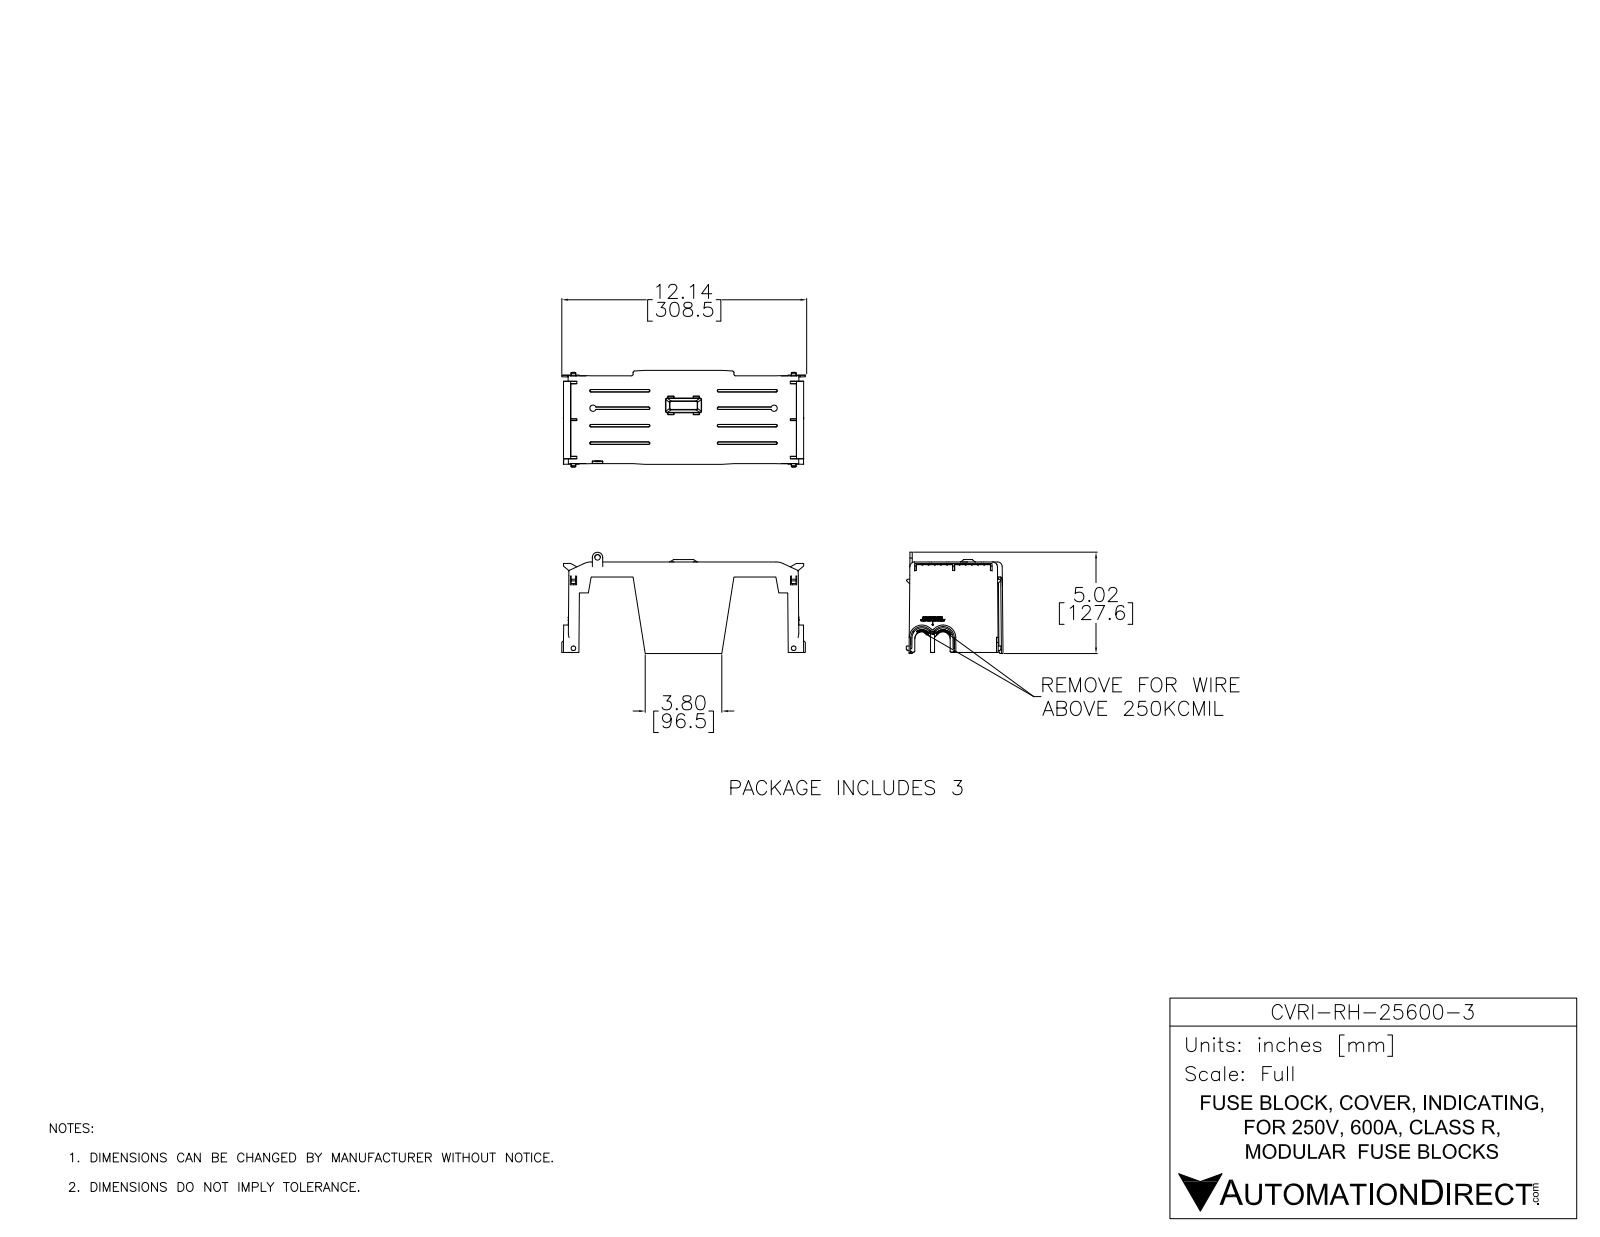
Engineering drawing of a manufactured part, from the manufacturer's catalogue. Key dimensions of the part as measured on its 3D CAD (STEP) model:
Part name (STEP PRODUCT): CVRI-RH-25600-3
STEP written by: SolidWorks 2017 (AUTOMOTIVE_DESIGN)
Units: inches
Bodies: 1 solid, 2344 faces (1576 planar, 119 cylindrical, 649 other)
Overall size (bounding box): 12.076 × 5.026 × 4.796
Volume: 12.93 in³ · Surface area: 333.4 in²
Round holes (diameter × count): ⌀0.276 ×1
Partial cylindrical surfaces — rounded edges, fillets, slot ends (radius × count): R0.039 ×18, R0.157 ×9, R0.118 ×8, R0.236 ×7, R0.079 ×4, R0.354 ×4, R0.492 ×4, R0.551 ×4
Main face-to-face distances: 0.079, 0.236, 0.157, 0.315, 0.197, 0.118, 0.795, 2.52, 0.158, 0.866
